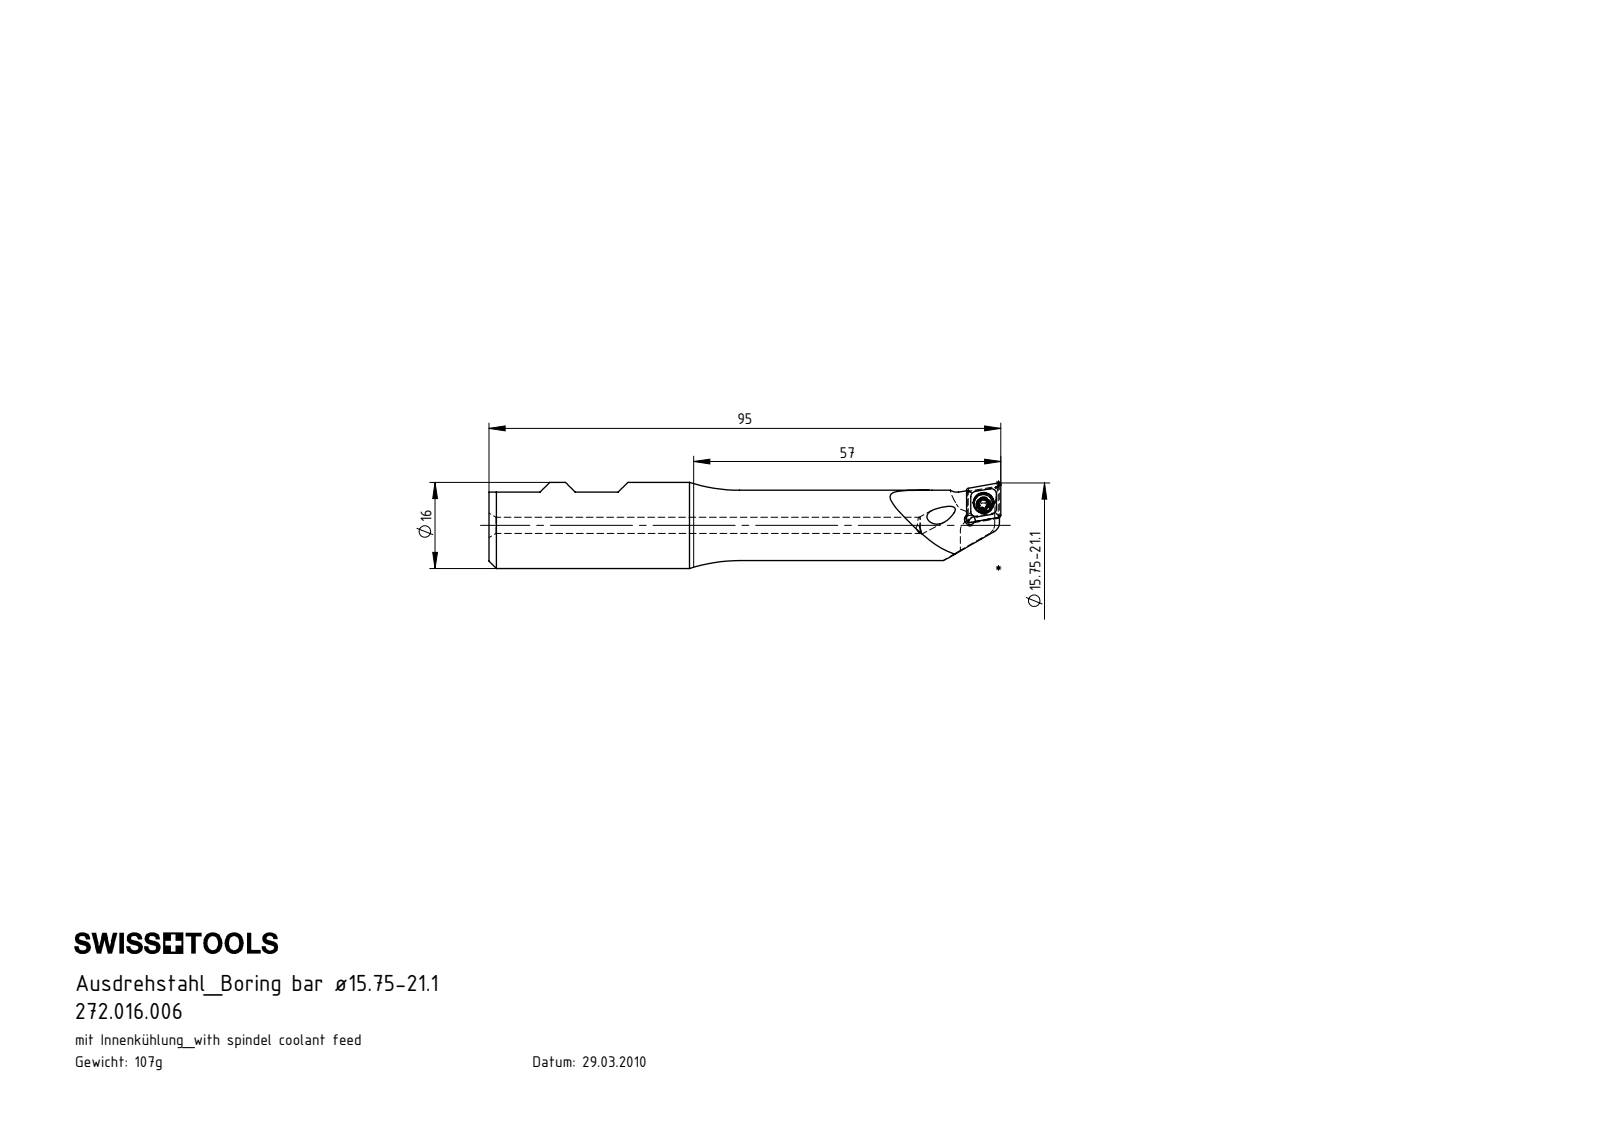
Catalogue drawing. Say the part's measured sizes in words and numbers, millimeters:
The part is named "B16-WCA.K11.095; CCMT060204; WCA-ER2.001.006_A; B16-WCA.K11.095_A". Its 3-D file was written by "SolidWorks 2015 (CONFIG_CONTROL_DESIGN)". It is 3 solids with 128 faces: 33 planar, 39 cylindrical and 56 other. Overall it measures 95 by 16 by 16 millimeters. Its volume is 13 562 cubic millimeters and its surface area 5 384 square millimeters. Round holes: 2 of diameter 3, 1 of diameter 2, 1 of diameter 2.05, 1 of diameter 2.8, 1 of diameter 3.85. Round bosses or shafts: 1 of diameter 16, 1 of diameter 13.05, 1 of diameter 3.4, 1 of diameter 2.5. Partial cylindrical surfaces (rounded edges, fillets, slot ends): 6 of radius 0.21, 5 of radius 0.36, 1 of radius 0.36, 1 of radius 2, 1 of radius 6.7, 1 of radius 7.5, 1 of radius 8. The main face-to-face distances are 2.18, 10.25, 5.28, 7.46, 7.66, 2.38, 88.76, 6.76, 1.48, 0.7. The hole center spacings are 3.89, 4.
